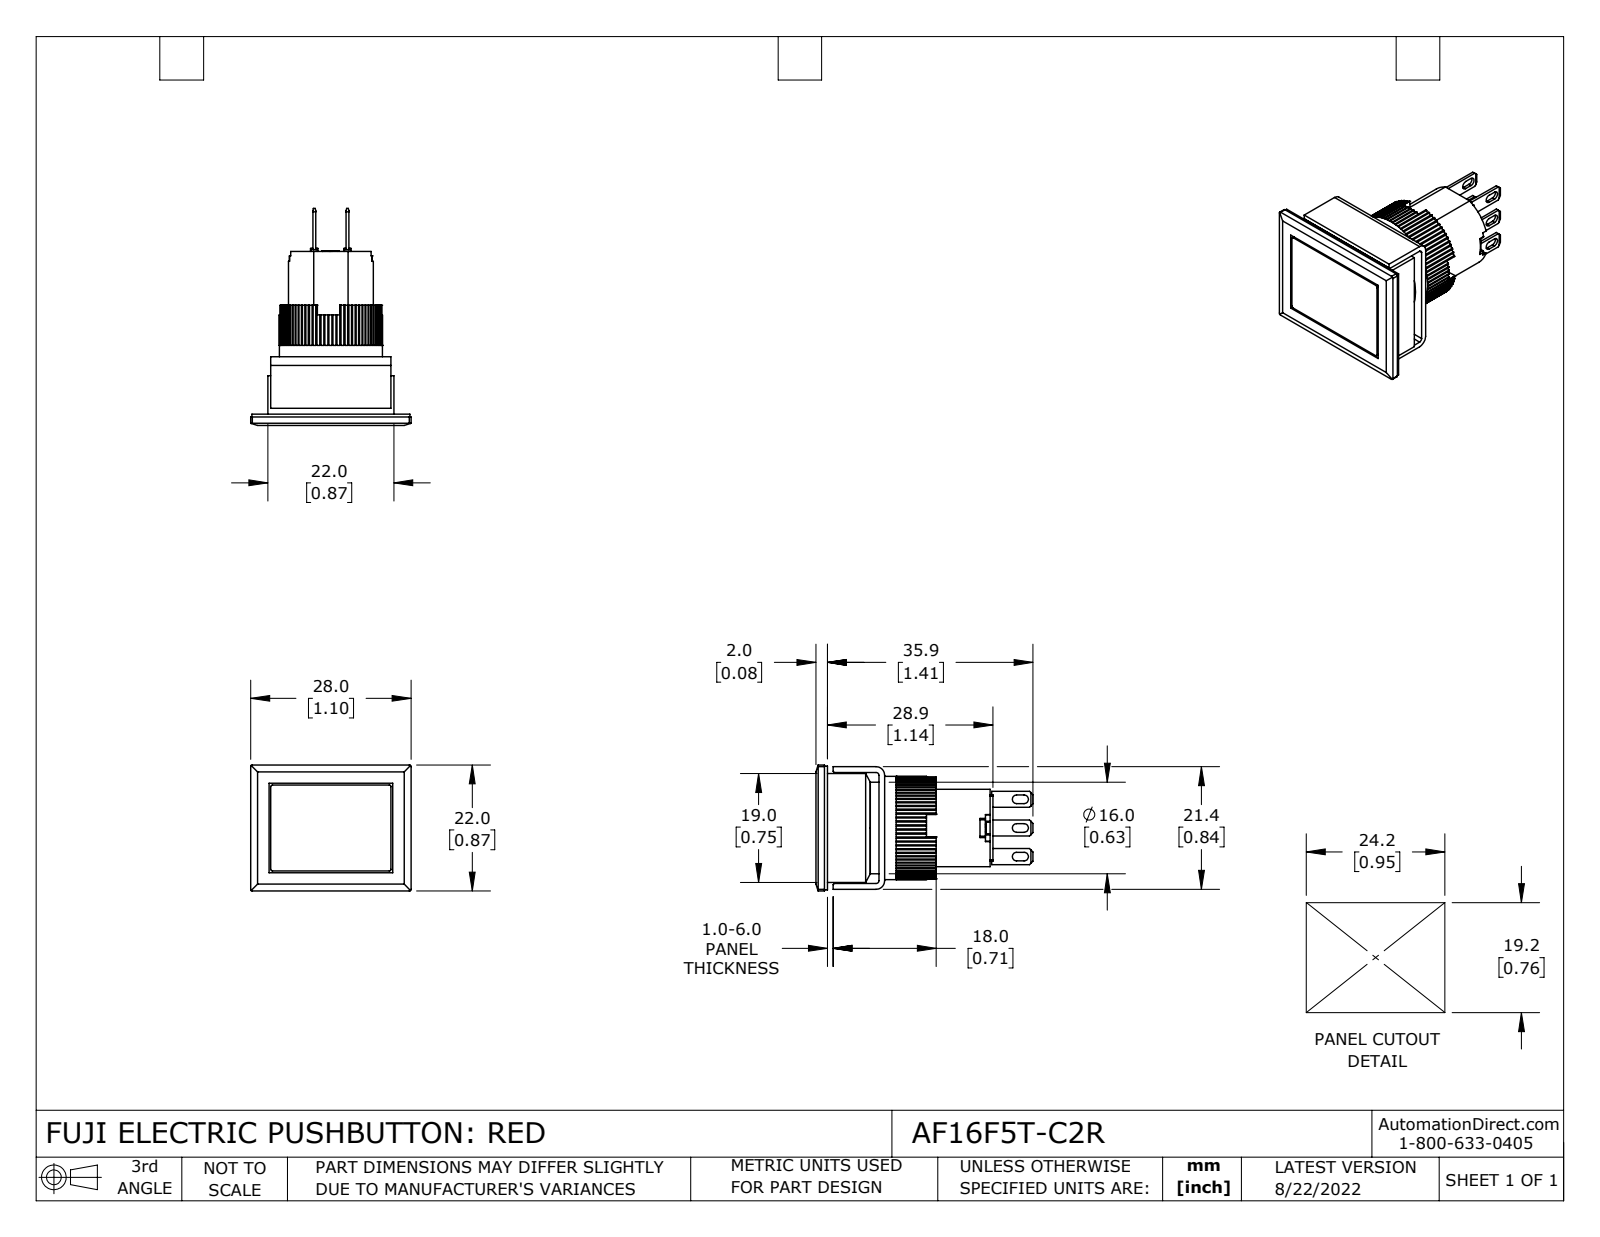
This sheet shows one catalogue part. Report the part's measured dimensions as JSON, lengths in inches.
{"part_name": "AF16F5T-C2R", "step_written_by": "SolidWorks 2021 (CONFIG_CONTROL_DESIGN)", "units": "inches", "bodies": {"solids": 12, "faces": 798, "planar": 620, "cylindrical": 176, "other": 2}, "overall_size": [1.492, 1.102, 0.866], "volume_in3": 0.541, "surface_area_in2": 11.85, "round_holes": [[0.039, 1], [0.709, 1]], "round_bosses_or_shafts": [[0.63, 1], [0.583, 1]], "partial_cylinders_radius": [[0.01, 80], [0.008, 12], [0.012, 8], [0.03, 6], [0.02, 2], [0.059, 2]], "face_to_face_distances": [0.374, 0.059, 0.02, 0.142, 0.039, 0.315, 0.232, 0.083, 0.079, 0.756]}
